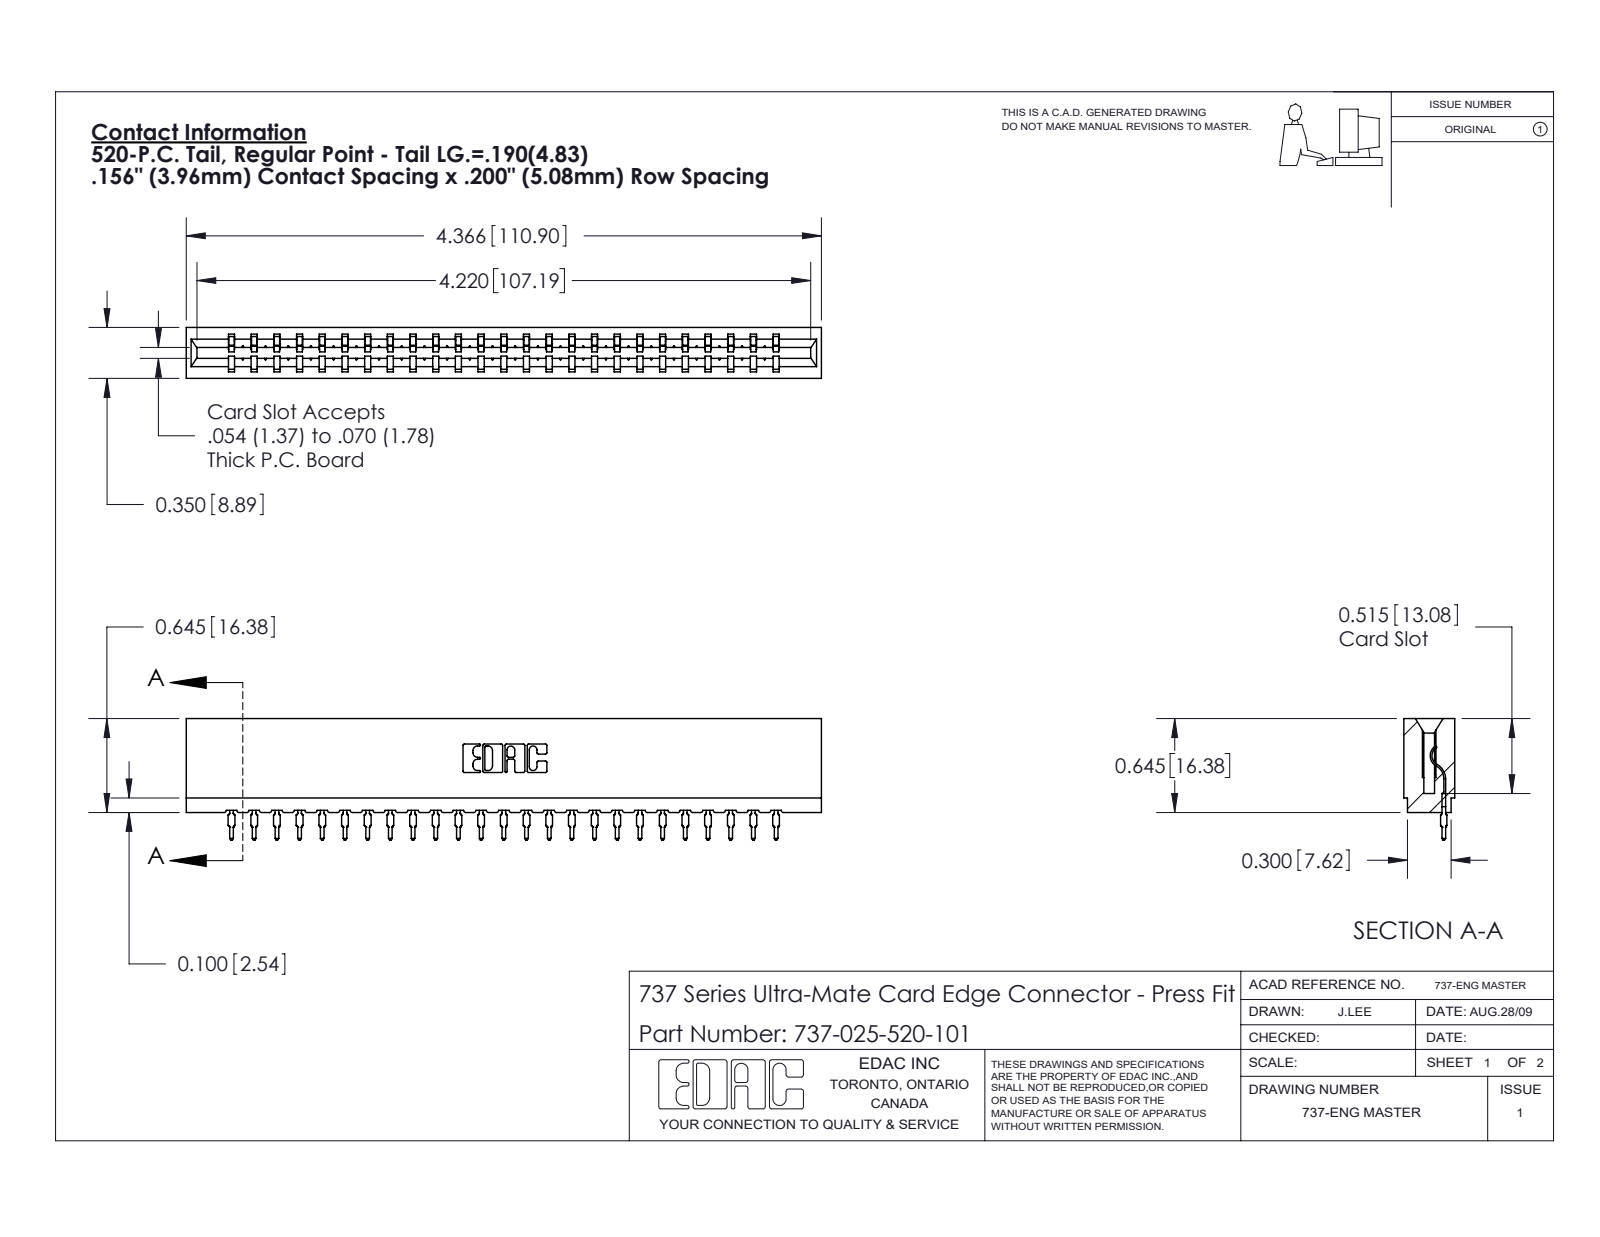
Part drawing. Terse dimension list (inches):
name: 737 Part_Insulator Option - 01; 745-292-001_520; 737-025-520-101
written by: SolidWorks 2020 (CONFIG_CONTROL_DESIGN)
unit: in
bodies: 26 solids, 2919 faces (1754 planar, 515 cylindrical, 650 other)
size: 4.366 × 0.836 × 0.35
volume: 0.659 in³; area: 21.75 in²
rounds: 50× R0.015, 50× R0.021, 22× R0.01, 6× R0.007, 6× R0.031, 4× R0.005, 4× R0.011, 3× R0.026
face distances: 0.138, 0.212, 0.35, 0.156, 0.624, 0.074, 0.468, 0.78, 0.045, 0.305
